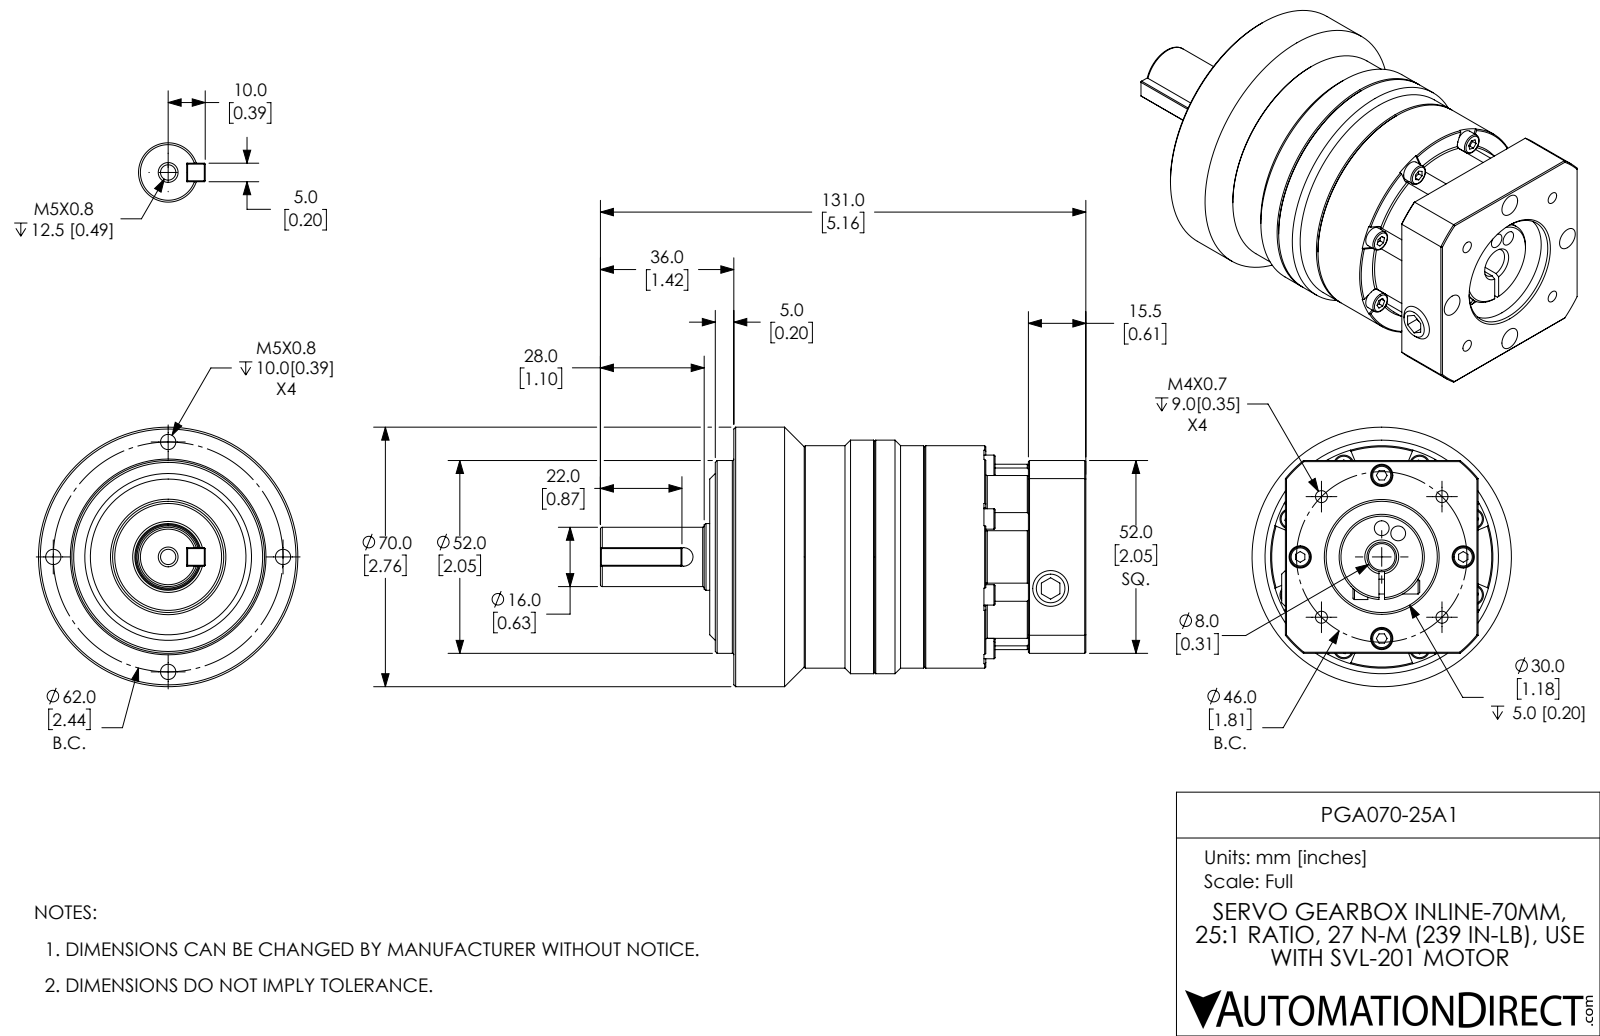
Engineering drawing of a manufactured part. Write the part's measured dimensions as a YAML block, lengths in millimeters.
part_name: "PGA070-25A1"
step_written_by: "SolidWorks 2019 (CONFIG_CONTROL_DESIGN)"
units: millimeters
bodies: {solids: 1, faces: 495, planar: 199, cylindrical: 129, other: 167}
overall_size: [131, 70, 70]
volume: 281581
surface_area: 37208
round_holes:
  - {diameter: 4.13, count: 5}
  - {diameter: 3.24, count: 4}
  - {diameter: 6, count: 4}
  - {diameter: 4, count: 2}
  - {diameter: 8, count: 2}
  - {diameter: 4.5, count: 1}
  - {diameter: 30, count: 1}
  - {diameter: 34, count: 1}
round_bosses_or_shafts:
  - {diameter: 5.5, count: 12}
  - {diameter: 70, count: 1}
  - {diameter: 63, count: 1}
  - {diameter: 60, count: 1}
  - {diameter: 52, count: 1}
  - {diameter: 23, count: 1}
  - {diameter: 18, count: 1}
  - {diameter: 16, count: 1}
partial_cylinders:
  - {radius: 3.25, count: 8}
  - {radius: 2.5, count: 1}
  - {radius: 4, count: 1}
  - {radius: 25, count: 1}
  - {radius: 26.75, count: 1}
  - {radius: 33.5, count: 1}
face_to_face_distances: [95, 15.5, 79.5, 86, 52, 6.5, 101.5, 5, 1.5, 27]
hole_center_spacings: [17.24, 21.95, 38.01, 41.57, 49.98, 9, 22, 23]
